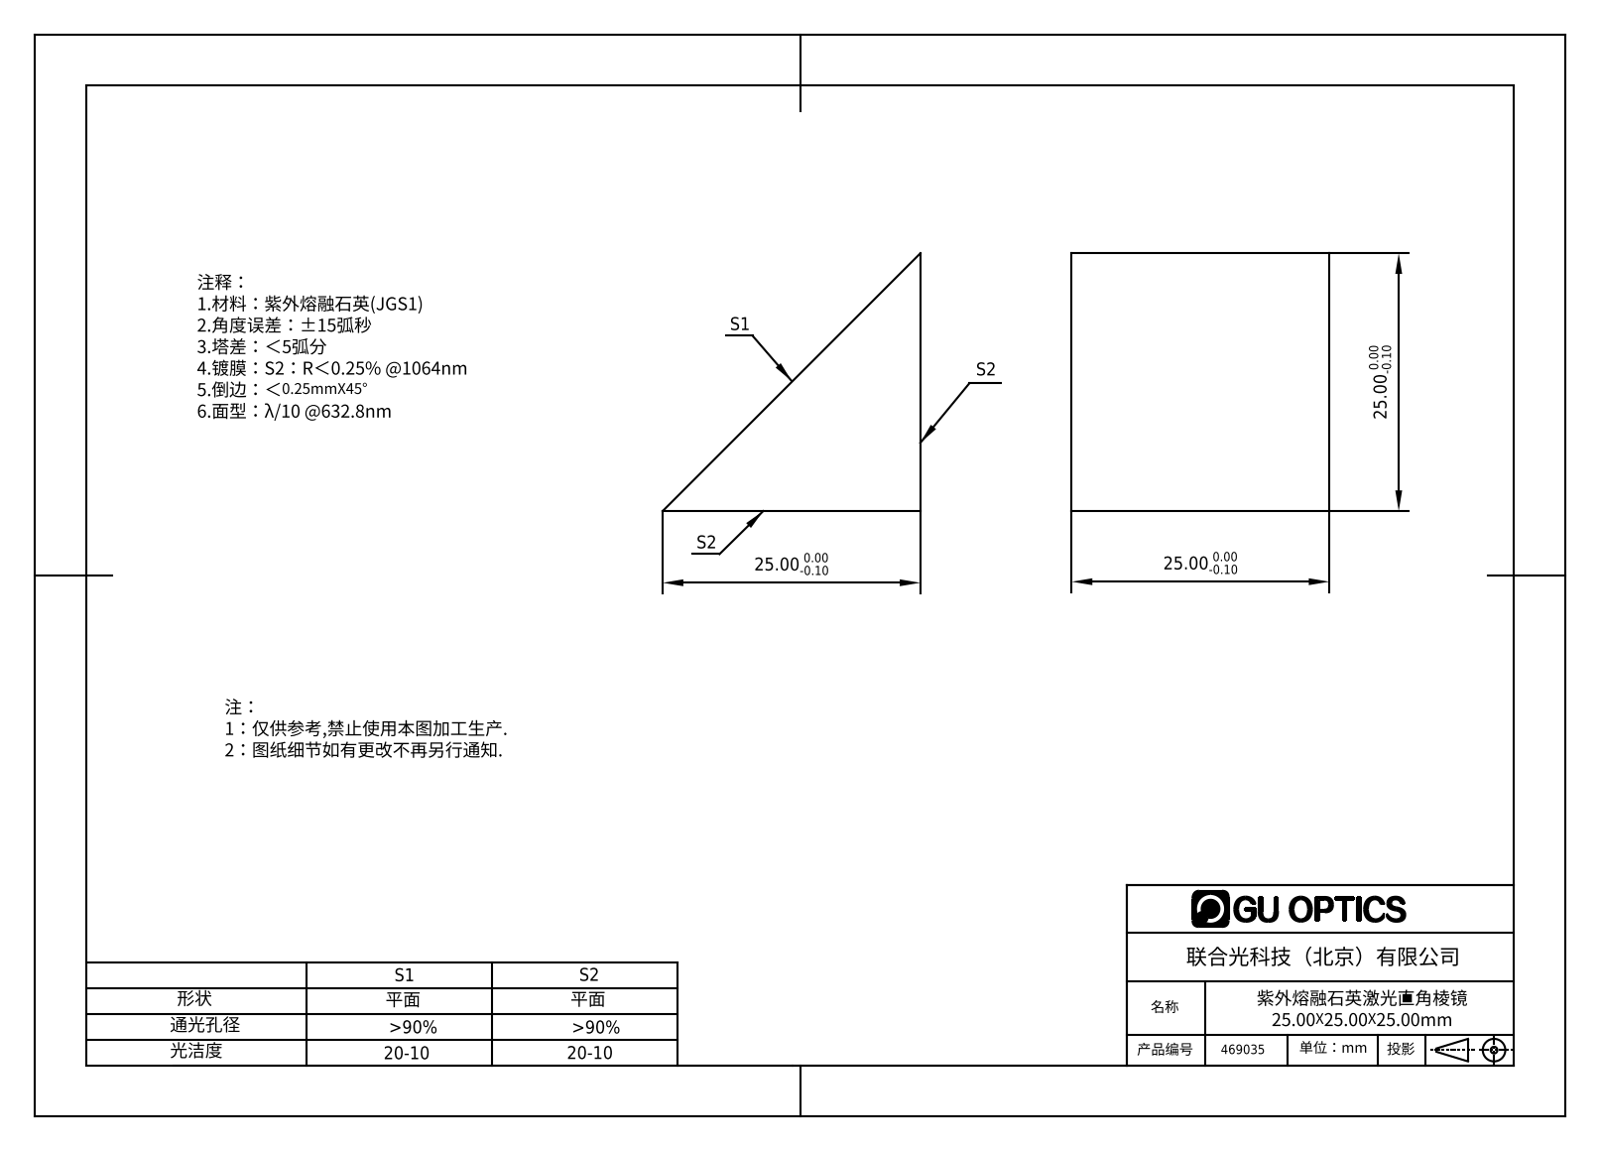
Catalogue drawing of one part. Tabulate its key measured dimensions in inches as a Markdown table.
| quantity | value |
| --- | --- |
| part name | 469005 |
| STEP written by | SolidWorks 2016 (AUTOMOTIVE_DESIGN) |
| units | inches |
| bodies | 1 solid, 5 faces (5 planar, 0 cylindrical, 0 other) |
| overall size | 1.235 × 0.984 × 0.821 |
| volume | 0.467 in³ |
| surface area | 4.108 in² |
| main face-to-face distances | 0.984 |
